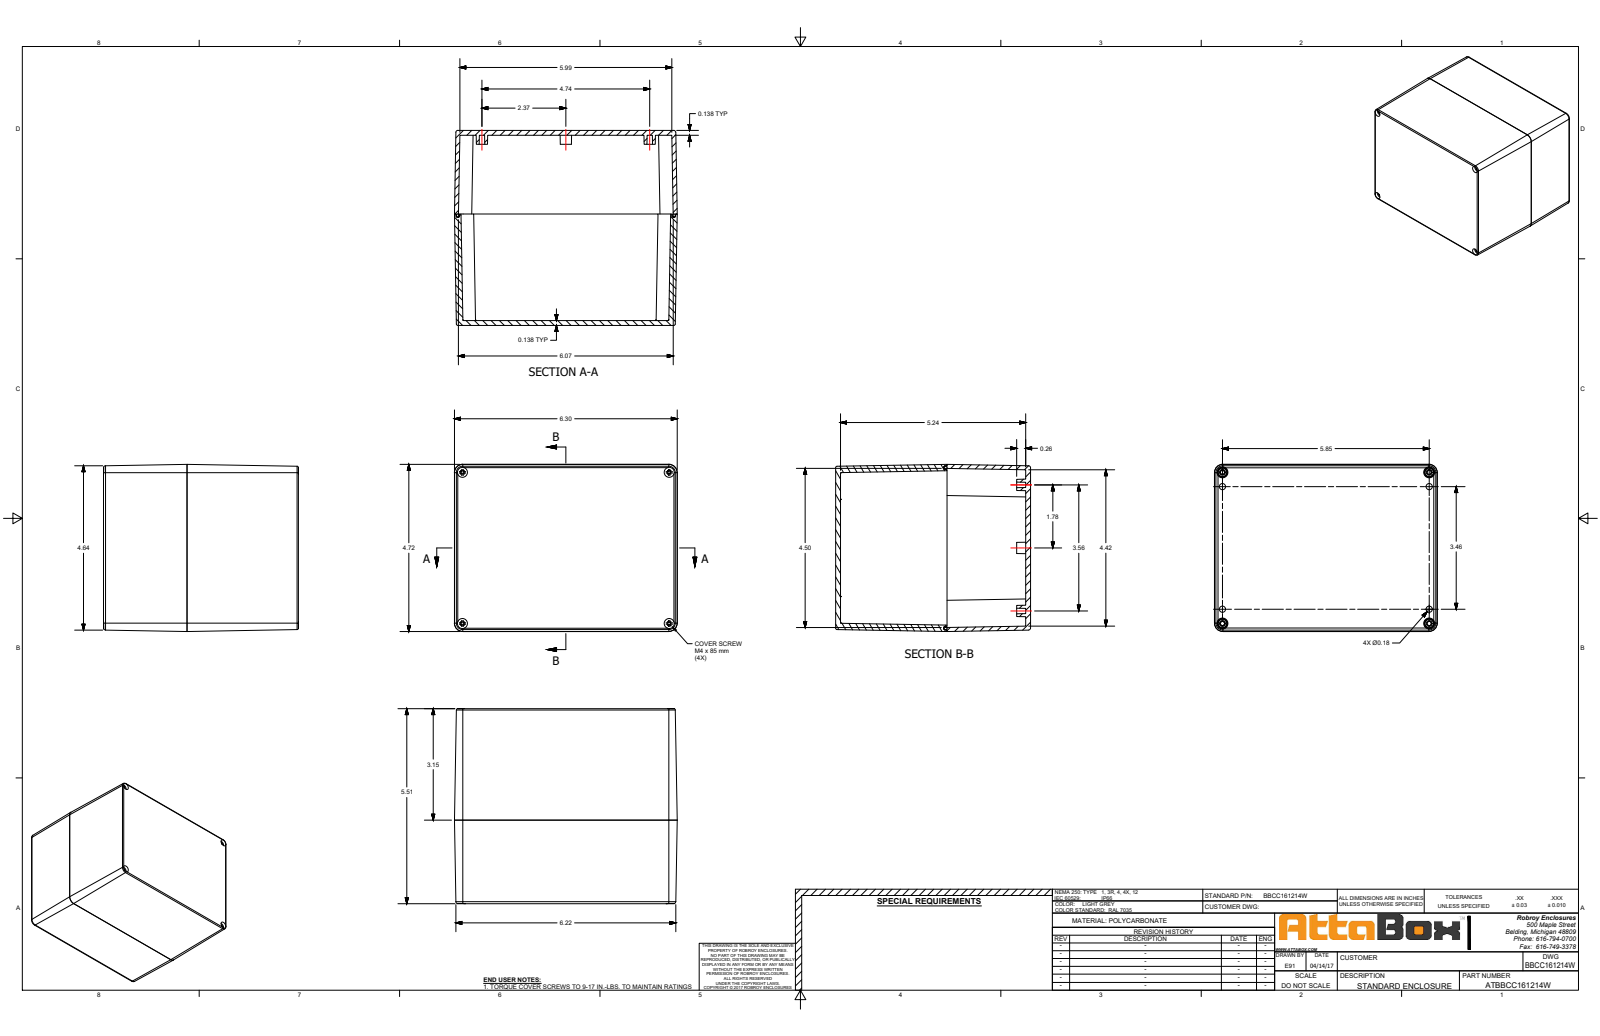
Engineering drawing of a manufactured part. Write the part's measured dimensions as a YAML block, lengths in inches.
part_name: "BBCC161214W"
step_written_by: "SolidWorks 2018 (AUTOMOTIVE_DESIGN)"
units: inches
bodies: {solids: 11, faces: 1479, planar: 599, cylindrical: 396, other: 484}
overall_size: [6.299, 5.512, 4.724]
volume: 27.09
surface_area: 407.5
round_holes:
  - {diameter: 0.177, count: 8}
  - {diameter: 0.128, count: 4}
  - {diameter: 0.189, count: 4}
  - {diameter: 0.201, count: 4}
  - {diameter: 0.276, count: 4}
  - {diameter: 0.283, count: 4}
  - {diameter: 0.307, count: 4}
round_bosses_or_shafts:
  - {diameter: 0.173, count: 4}
  - {diameter: 0.157, count: 4}
  - {diameter: 0.13, count: 4}
partial_cylinders:
  - {radius: 0.039, count: 40}
  - {radius: 0.02, count: 30}
  - {radius: 0.098, count: 8}
  - {radius: 0.193, count: 8}
  - {radius: 0.059, count: 4}
  - {radius: 0.102, count: 4}
  - {radius: 0.124, count: 4}
  - {radius: 0.126, count: 4}
face_to_face_distances: [0.138, 5.374, 0.114, 0.181, 5.512, 4.543, 4.724, 5.236, 4.429, 4.61]
hole_center_spacings: [0.404, 3.868, 5.846, 5.86, 7.01, 3.465, 4.272, 6.796]
